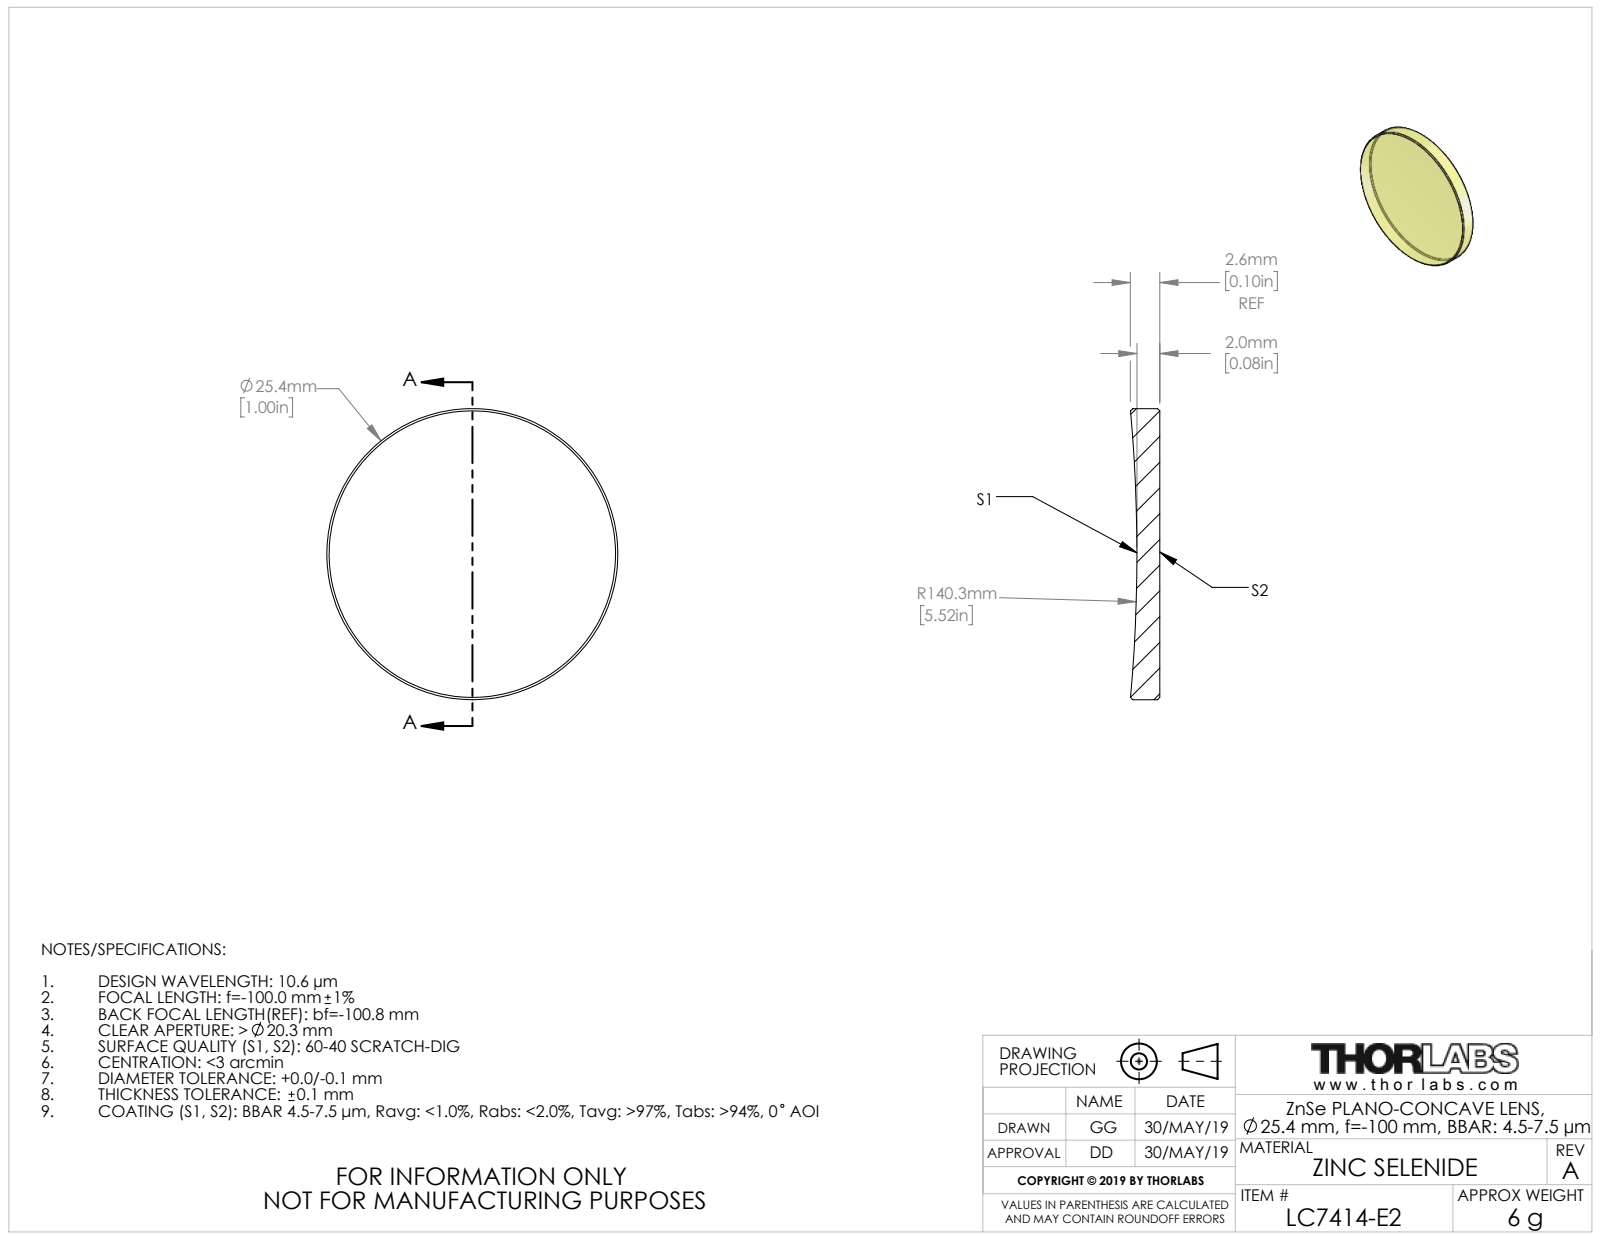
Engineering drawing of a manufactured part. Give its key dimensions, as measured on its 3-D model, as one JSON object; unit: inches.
{"part_name": "TTN047630-E0W", "step_written_by": "SolidWorks 2018 (CONFIG_CONTROL_DESIGN)", "units": "inches", "bodies": {"solids": 1, "faces": 9, "planar": 1, "cylindrical": 2, "other": 6}, "overall_size": [1, 1, 0.101], "volume_in3": 0.071, "surface_area_in2": 1.86, "round_bosses_or_shafts": [[1, 1]]}
